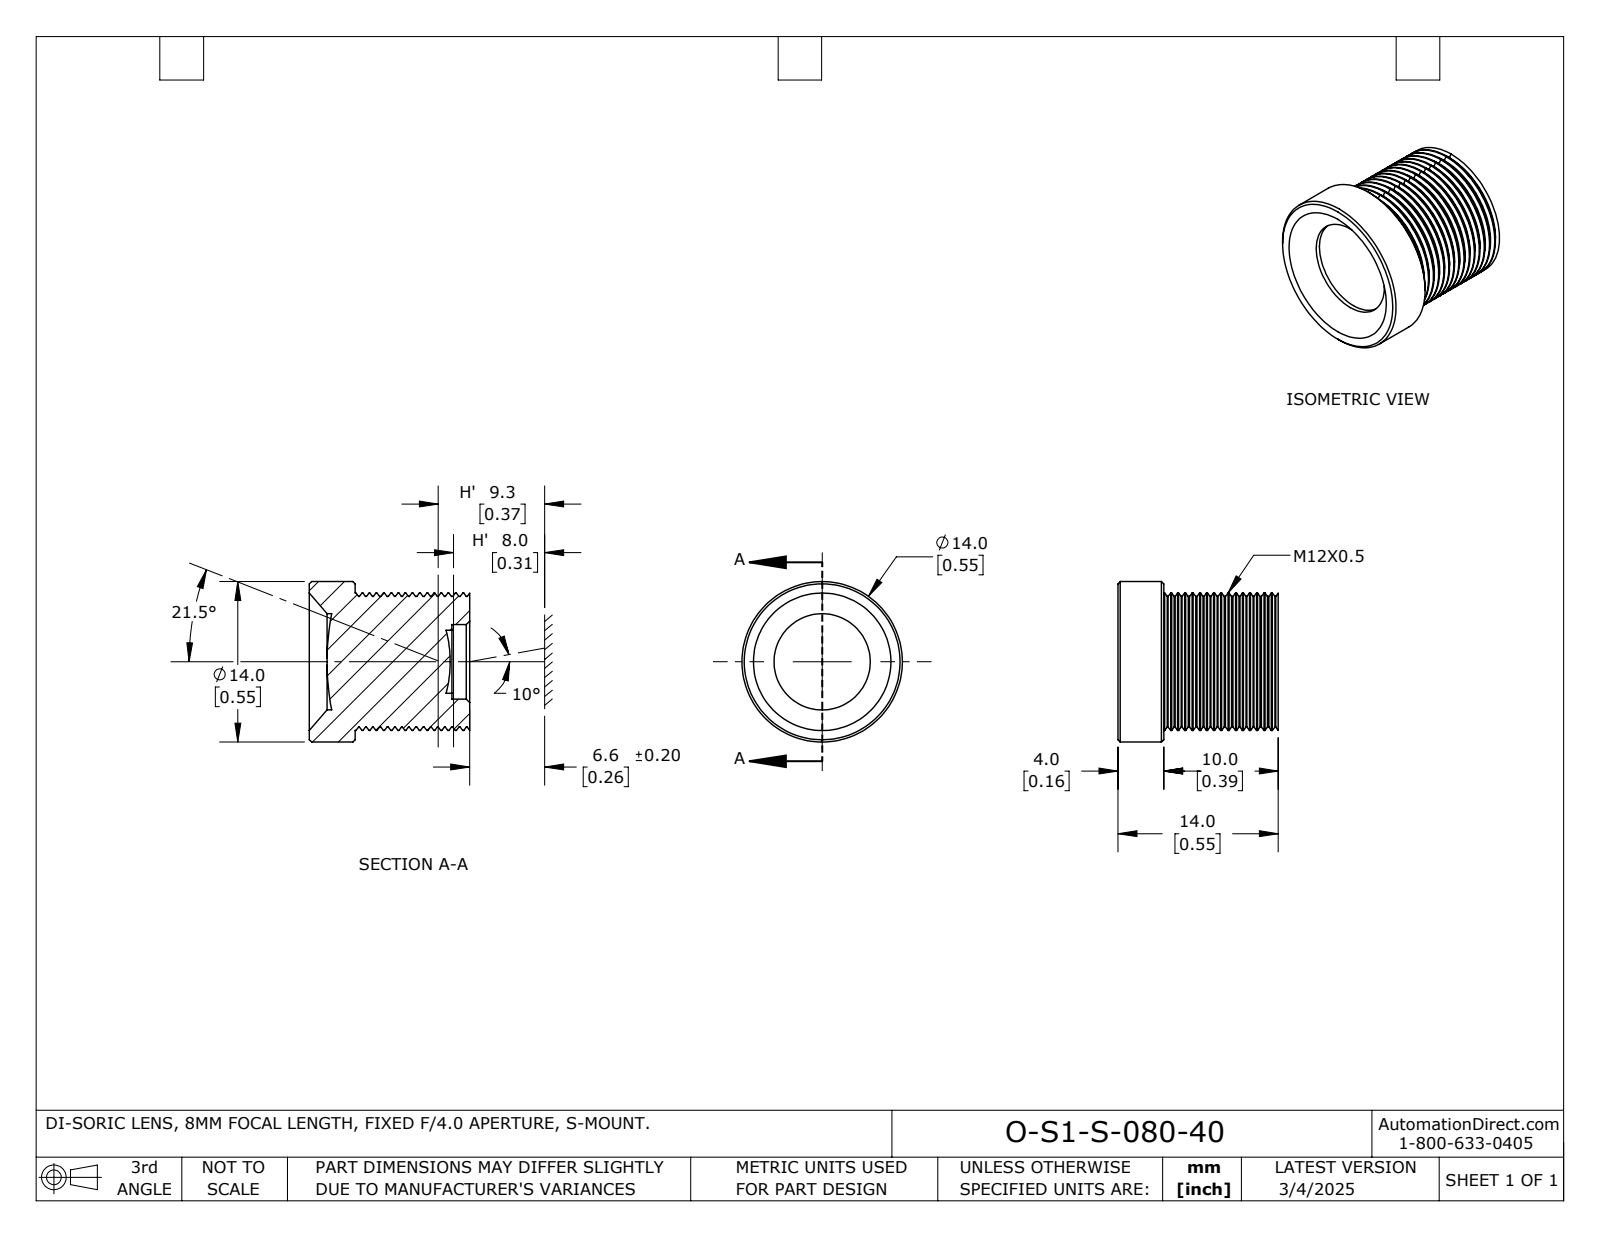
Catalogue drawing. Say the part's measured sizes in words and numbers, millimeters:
The part is named "O-S1-S-080-40 -- 213096". Its 3-D file was written by "SolidWorks 2024 (AUTOMOTIVE_DESIGN)". It is 1 solid with 152 faces: 4 planar, 72 cylindrical and 76 other. Overall it measures 14 by 14 by 13.99 millimeters. Its volume is 1 490 cubic millimeters and its surface area 1 083 square millimeters. Round holes: 1 of diameter 5.5, 1 of diameter 6.5, 1 of diameter 8.4. Round bosses or shafts: 1 of diameter 14, 1 of diameter 12, 1 of diameter 11.4. The main face-to-face distances are 14, 4, 10, 12.45, 8.45, 1.55.
